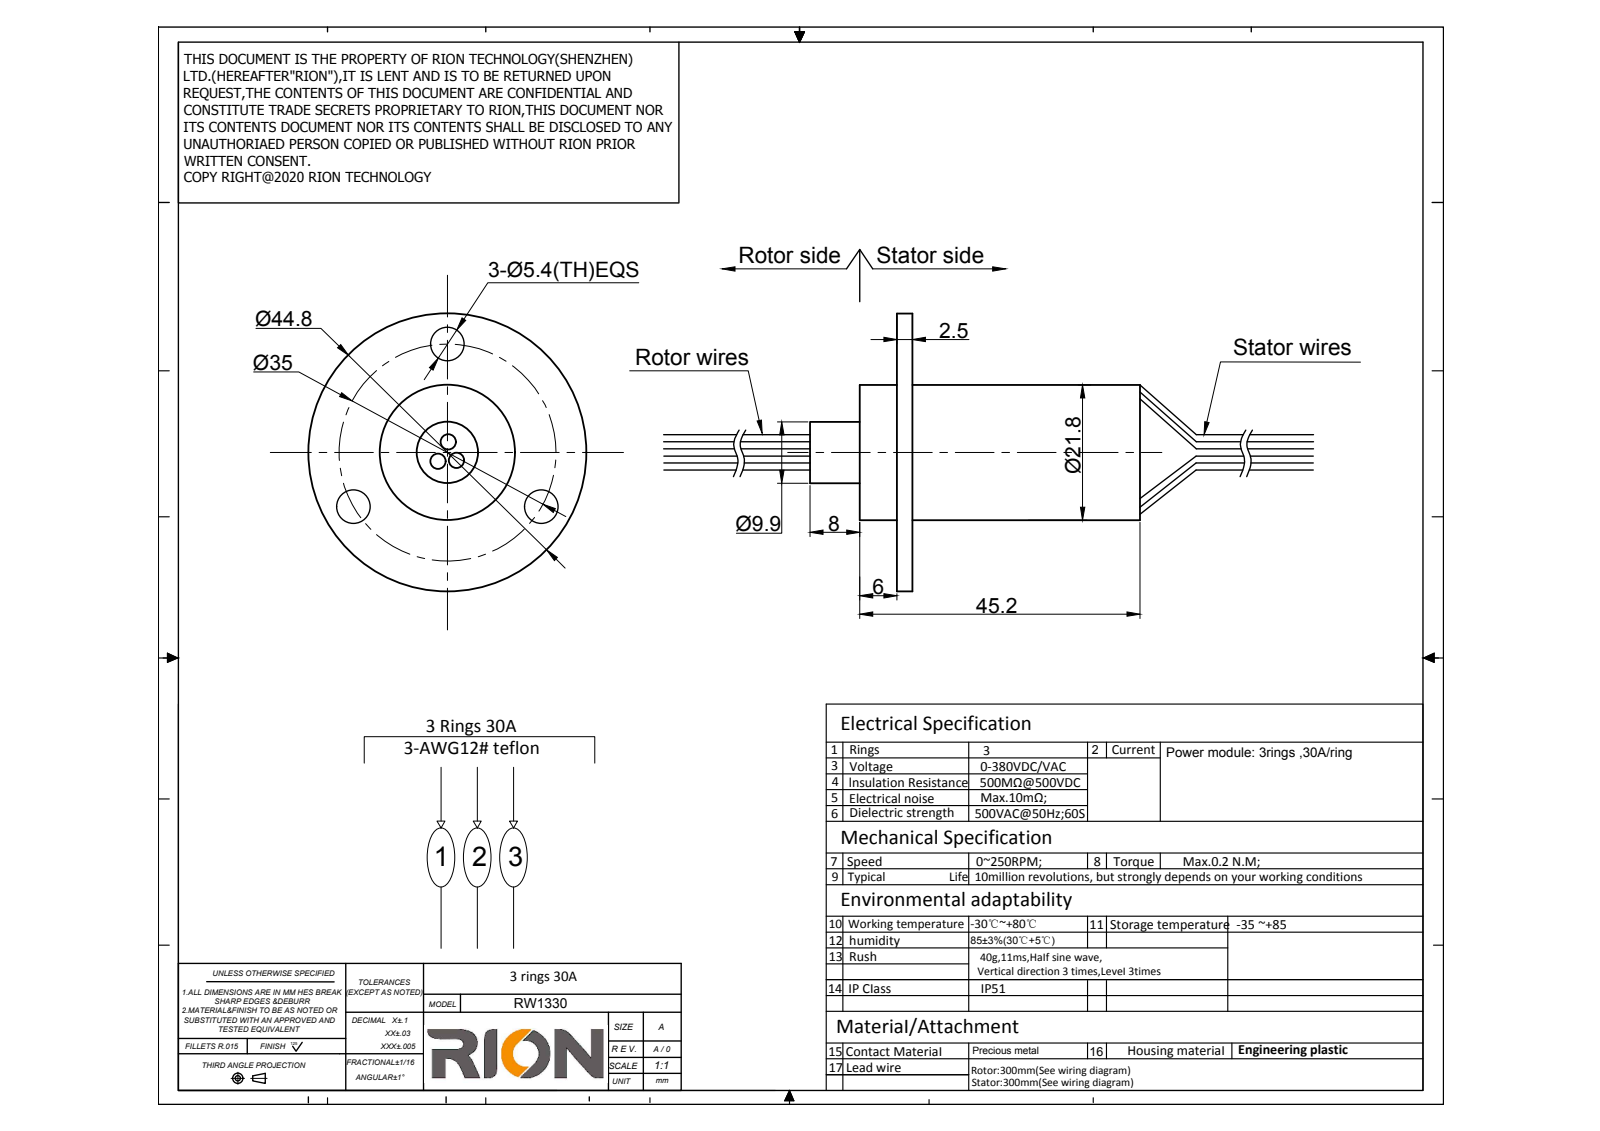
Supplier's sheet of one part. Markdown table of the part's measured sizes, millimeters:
| quantity | value |
| --- | --- |
| part name | RW1320 |
| STEP written by | SolidWorks 2014 (CONFIG_CONTROL_DESIGN) |
| units | millimeters |
| bodies | 1 solid, 64 faces (30 planar, 34 cylindrical, 0 other) |
| overall size | 92.7 × 44.8 × 44.8 |
| volume | 22 047 mm³ |
| surface area | 8 205 mm² |
| round holes (diameter × count) | 5.4 × 3, 7.36 × 1, 10.1 × 1, 20 × 1 |
| round bosses / shafts (diameter × count) | 3.2 × 6, 44.8 × 1, 22 × 1, 19.9 × 1, 9.9 × 1 |
| main face-to-face distances | 3, 39, 36, 6, 9, 45, 20, 72.7, 8, 14 |
| hole center spacings | 17.5, 30.31, 30.32 |
